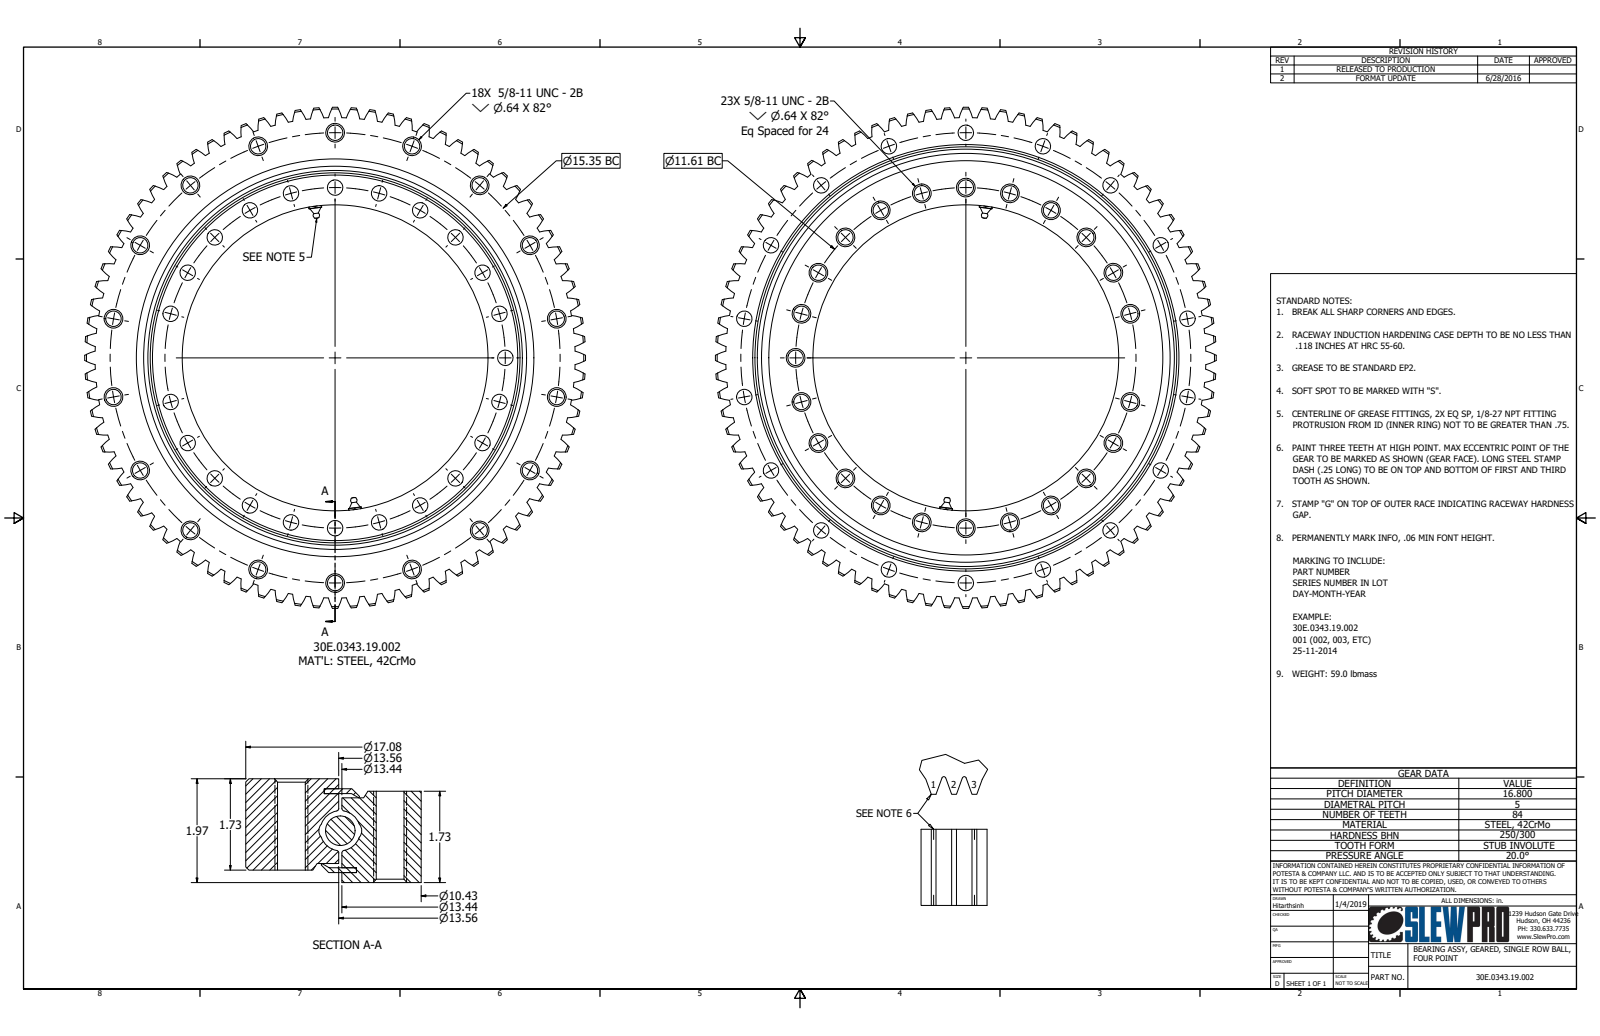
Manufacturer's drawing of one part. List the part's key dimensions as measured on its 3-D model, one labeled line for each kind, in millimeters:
Part name (STEP PRODUCT): 30E.0343.19.002; Spur Gears1; 1_8 NPT Fitting
STEP written by: Autodesk Inventor 2019 (AUTOMOTIVE_DESIGN)
Units: millimetres
Bodies: 7 solids, 815 faces (38 planar, 397 cylindrical, 380 other)
Overall size (bounding box): 434 × 434 × 50
Volume: 3 410 000 mm³ · Surface area: 662 600 mm²
Round holes (diameter × count): ⌀13.4 ×41, ⌀2.5 ×2, ⌀22.3 ×1, ⌀265 ×1, ⌀327.4 ×1, ⌀344.4 ×1, ⌀358.4 ×1
Round bosses / shafts (diameter × count): ⌀358.4 ×1, ⌀341.4 ×1, ⌀327.4 ×1, ⌀22.2 ×1
Partial cylindrical surfaces — rounded edges, fillets, slot ends (radius × count): R52.2 ×168, R208 ×1, R217 ×1
Main face-to-face distances: 38, 1.2, 44, 6, 50, 1.2, 2.4, 4.8, 45.2, 39.2
Hole centre spacings: 147.5, 76.4, 285, 179.6, 272.5, 292.5, 38.5, 112.9
